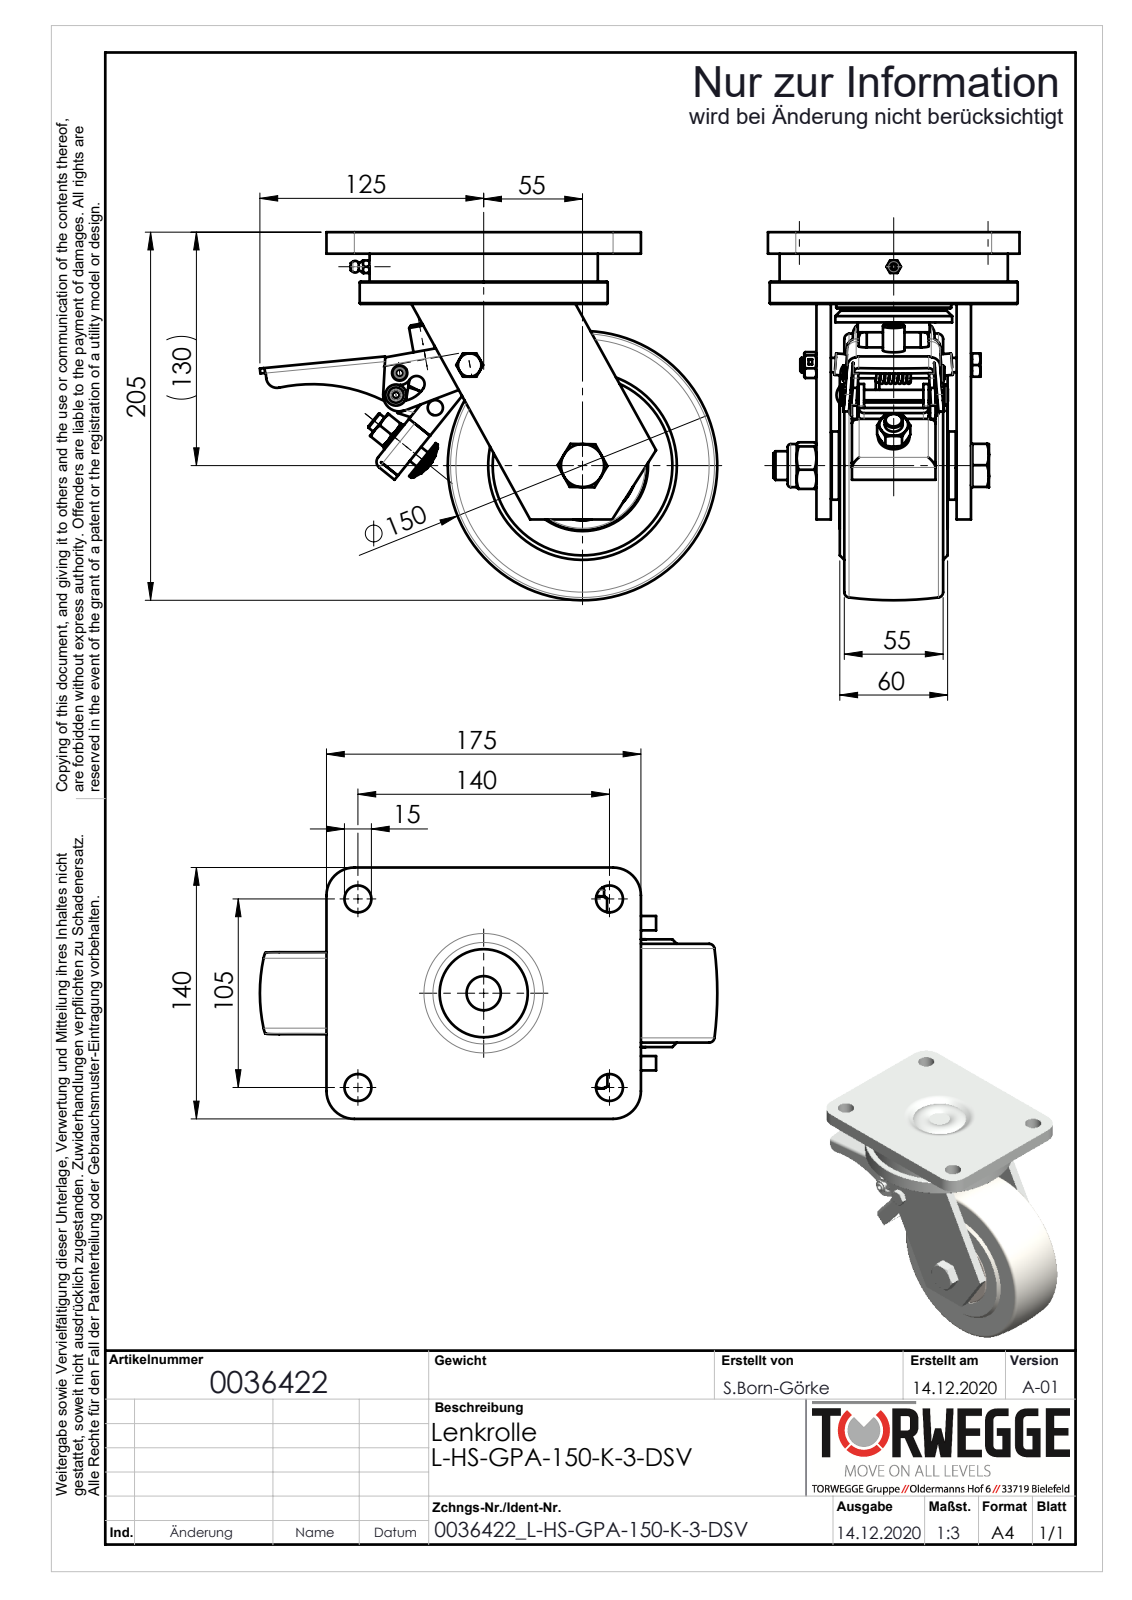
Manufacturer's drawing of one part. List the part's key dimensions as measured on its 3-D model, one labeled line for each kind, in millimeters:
Part name (STEP PRODUCT): 0036422
STEP written by: SolidWorks 2018 (AUTOMOTIVE_DESIGN)
Units: millimetres
Bodies: 51 solids, 943 faces (292 planar, 349 cylindrical, 302 other)
Overall size (bounding box): 254.56 × 205 × 140
Volume: 1 793 000 mm³ · Surface area: 415 378 mm²
Round holes (diameter × count): ⌀6 ×7, ⌀15 ×4, ⌀4 ×3, ⌀8.4 ×2, ⌀8.5 ×2, ⌀30 ×2, ⌀5 ×1, ⌀5.8 ×1, ⌀6.3 ×1, ⌀6.8 ×1, ⌀8 ×1, ⌀8.2 ×1
Round bosses / shafts (diameter × count): ⌀12 ×3, ⌀8.5 ×3, ⌀24 ×2, ⌀6 ×2, ⌀5.8 ×2, ⌀2 ×2, ⌀138 ×1, ⌀127 ×1
Partial cylindrical surfaces — rounded edges, fillets, slot ends (radius × count): R4 ×7, R3 ×4, R4.25 ×4, R5.35 ×4, R15.5 ×4, R0.5 ×3, R6 ×3, R0.1 ×2
Main face-to-face distances: 15.5, 8, 78, 2.5, 40, 7.5, 13, 12, 5, 70.5
Hole centre spacings: 87.5, 12.44, 105, 140, 175, 12.42, 23, 27.69
